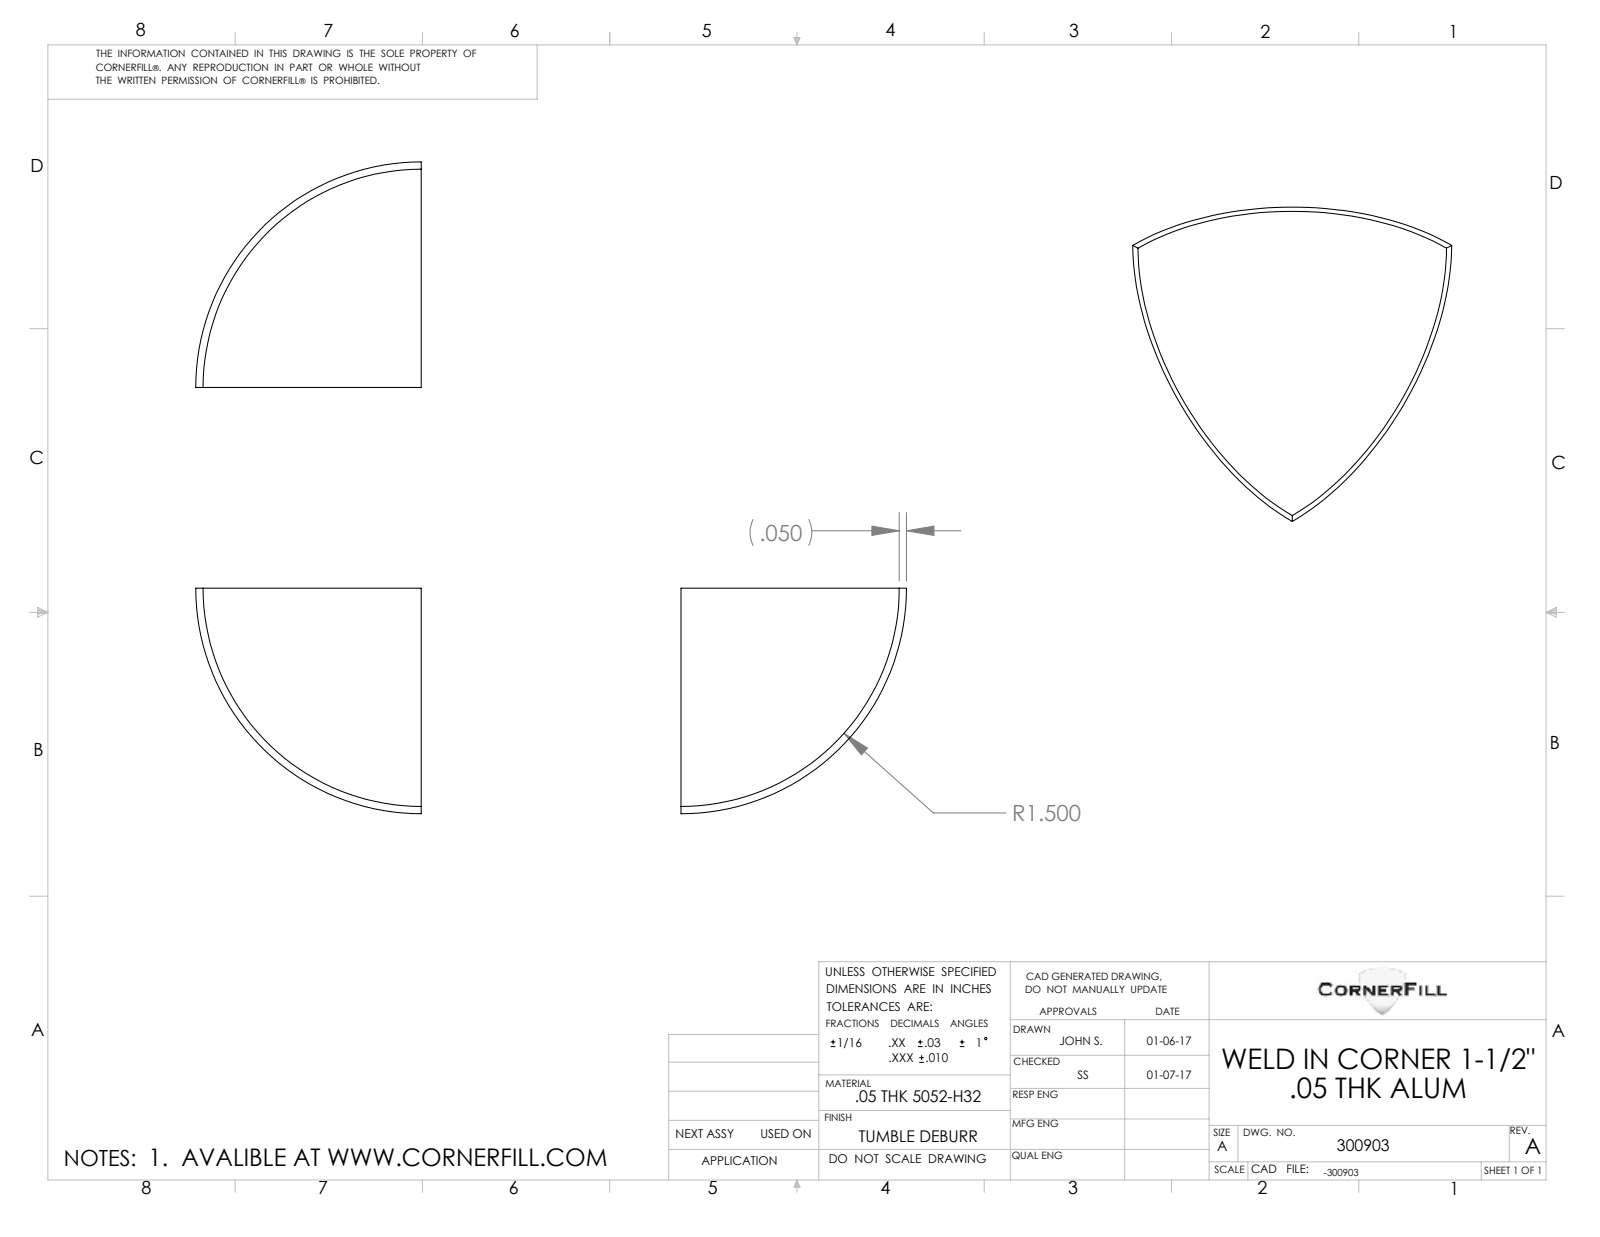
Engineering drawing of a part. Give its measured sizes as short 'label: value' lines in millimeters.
name: 300903
written by: SolidWorks 2016 (CONFIG_CONTROL_DESIGN)
unit: mm
bodies: 1 solid, 5 faces (3 planar, 0 cylindrical, 2 other)
size: 39.4 × 39.4 × 39.4
volume: 3 000 mm³; area: 4 946 mm²
